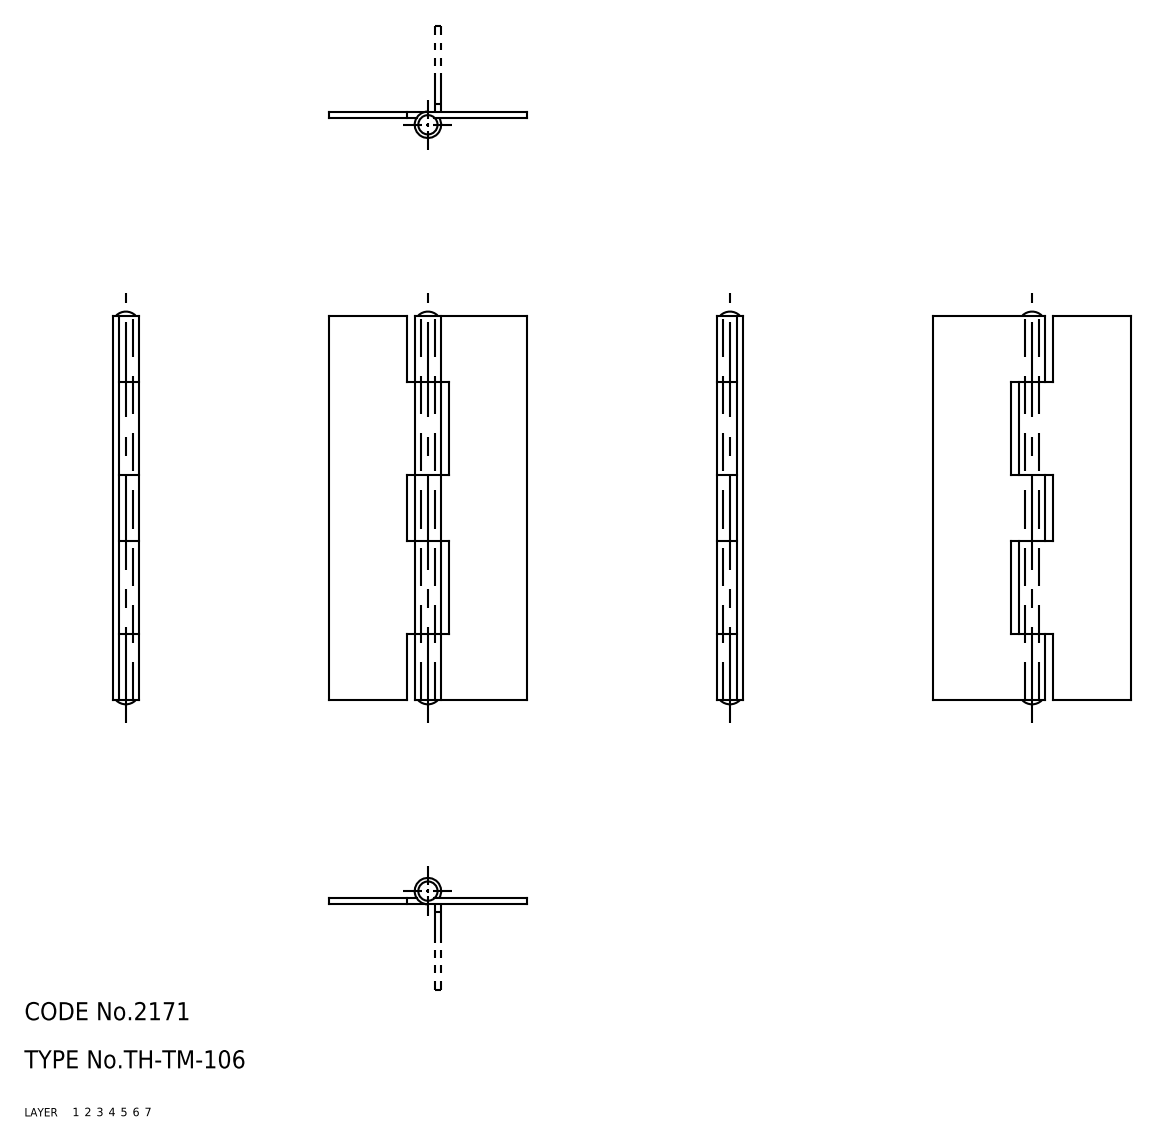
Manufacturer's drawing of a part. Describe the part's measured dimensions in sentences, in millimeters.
The part is named "67110934; 67110947; 67110960". Its 3-D file was written by "CADfix (AUTOMOTIVE_DESIGN)". It is 3 solids with 44 faces: 0 planar, 0 cylindrical and 44 other. Overall it measures 65.3 by 33 by 4.4 millimeters. Its volume is 2 756 cubic millimeters and its surface area 5 862 square millimeters.
